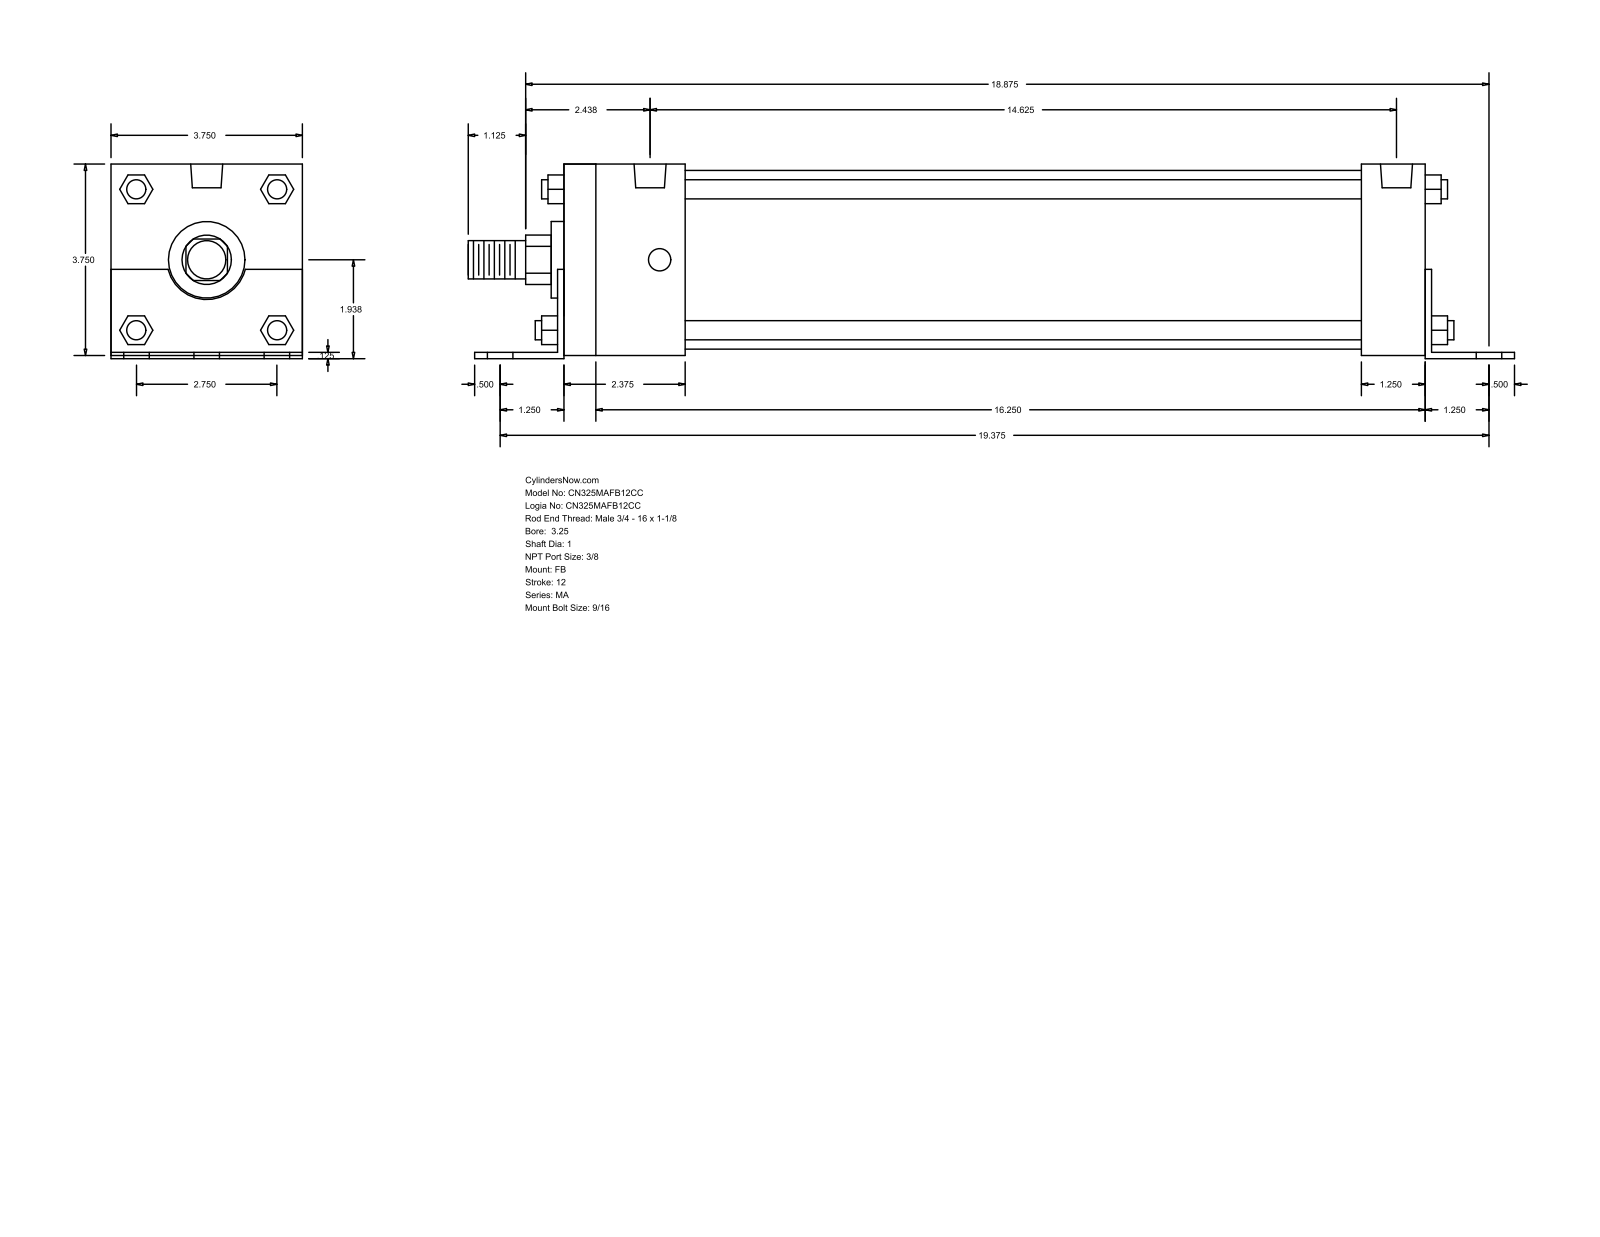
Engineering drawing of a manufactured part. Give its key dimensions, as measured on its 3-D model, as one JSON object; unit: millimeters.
{"part_name": "MA_FB__0325_1", "step_written_by": "GSSL Pune (CONFIG_CONTROL_DESIGN)", "units": "millimeters", "bodies": {"solids": 0, "faces": 140, "planar": 105, "cylindrical": 35, "other": 0}, "overall_size": [520.7, 96.84, 95.25], "round_holes": [[14.29, 6], [11.11, 4], [15.93, 2]], "round_bosses_or_shafts": [[9.53, 4], [88.9, 1], [38.1, 1], [25.4, 1], [19.05, 1]], "partial_cylinders_radius": [[12.29, 1], [19.81, 1]], "face_to_face_distances": [95.24, 3.17, 1.59, 96.83, 1.58, 93.66, 431.8, 428.63, 434.97, 400.05], "hole_center_spacings": [34.92, 493.37, 492.13, 57.78, 61.65, 69.84, 82.38, 86.71]}
